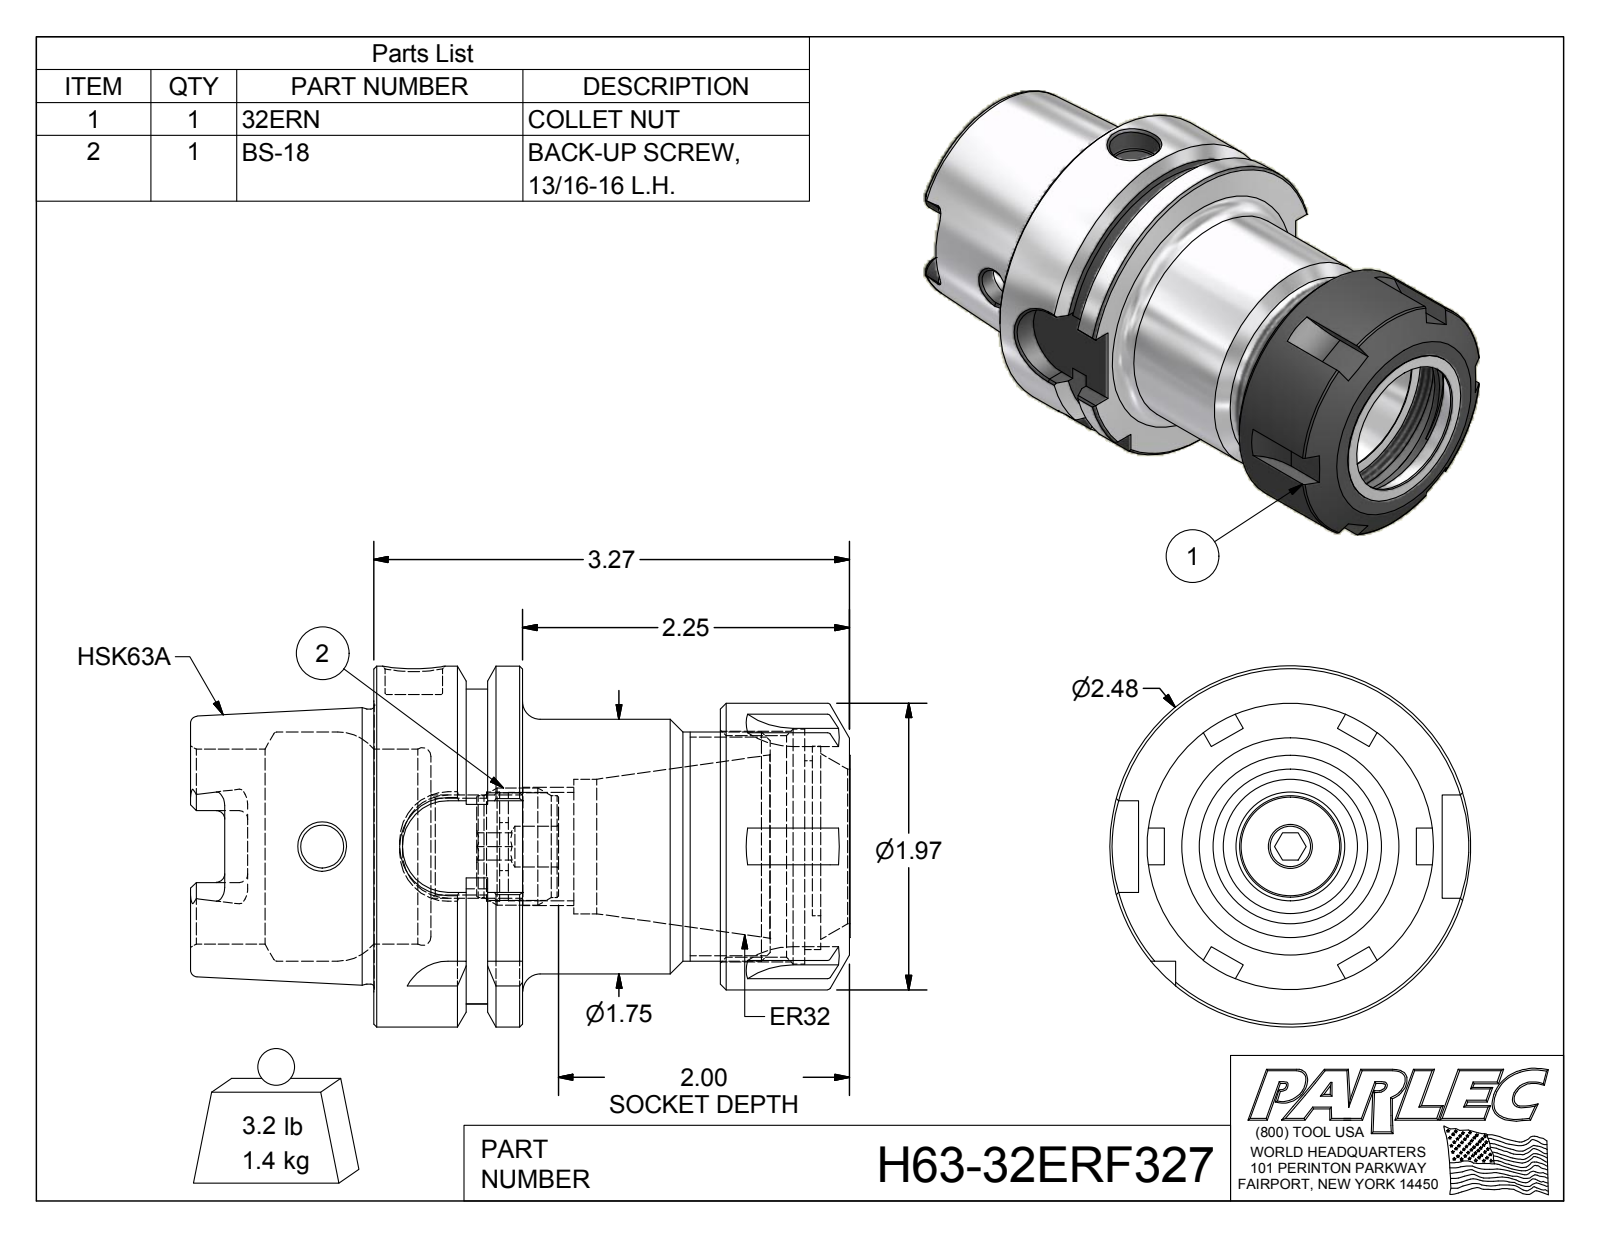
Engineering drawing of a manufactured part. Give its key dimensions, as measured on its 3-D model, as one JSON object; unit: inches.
{"part_name": "H63-32ER3-1; BS-18; 32ERN; H63-32ERF327", "step_written_by": "Autodesk Inventor 2016 (AUTOMOTIVE_DESIGN)", "units": "inches", "bodies": {"solids": 3, "faces": 241, "planar": 96, "cylindrical": 60, "other": 85}, "overall_size": [4.53, 2.48, 2.48], "volume_in3": 8.673, "surface_area_in2": 64.48, "round_holes": [[0.28, 1], [0.295, 1], [0.331, 1], [0.394, 1], [0.666, 1], [0.745, 1], [0.749, 1], [0.925, 1], [1.063, 1], [1.3, 1], [1.339, 1], [1.522, 1]], "round_bosses_or_shafts": [[2.48, 1], [1.969, 1], [1.891, 1], [1.75, 1], [0.805, 1], [0.7, 1]], "partial_cylinders_radius": [[0.02, 12], [0.059, 6], [0.113, 4], [0.315, 4], [0.587, 1], [0.689, 1], [1.083, 1]], "face_to_face_distances": [1.024, 0.241, 0.389, 3.27, 2.246, 0.394, 0.63, 2.876, 2.373, 1.98], "hole_center_spacings": [0.073]}
